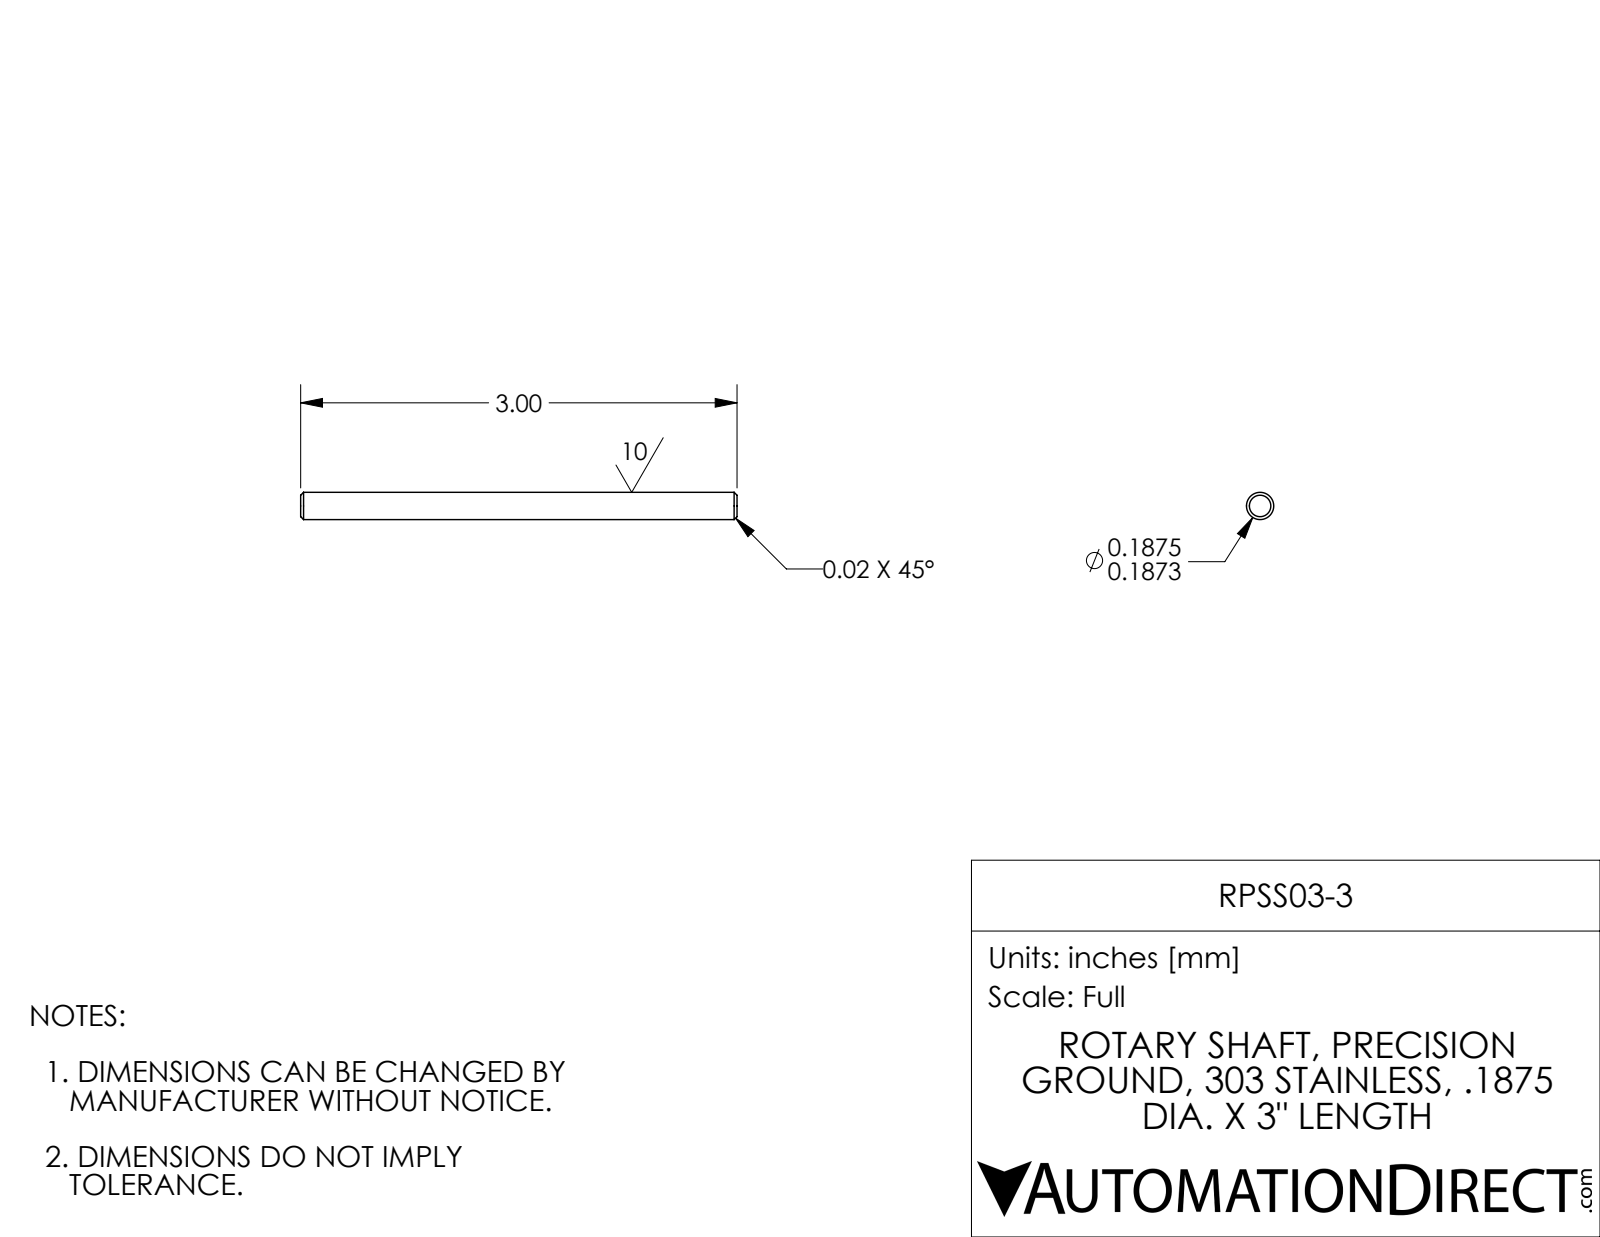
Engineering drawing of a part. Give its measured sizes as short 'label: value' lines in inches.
name: RPSS03-3
written by: SolidWorks 2017 (AUTOMOTIVE_DESIGN)
unit: in
bodies: 1 solid, 8 faces (2 planar, 2 cylindrical, 4 other)
size: 3 × 0.188 × 0.188
volume: 0.083 in³; area: 1.808 in²
bosses: 1× ⌀0.187
face distances: 3
